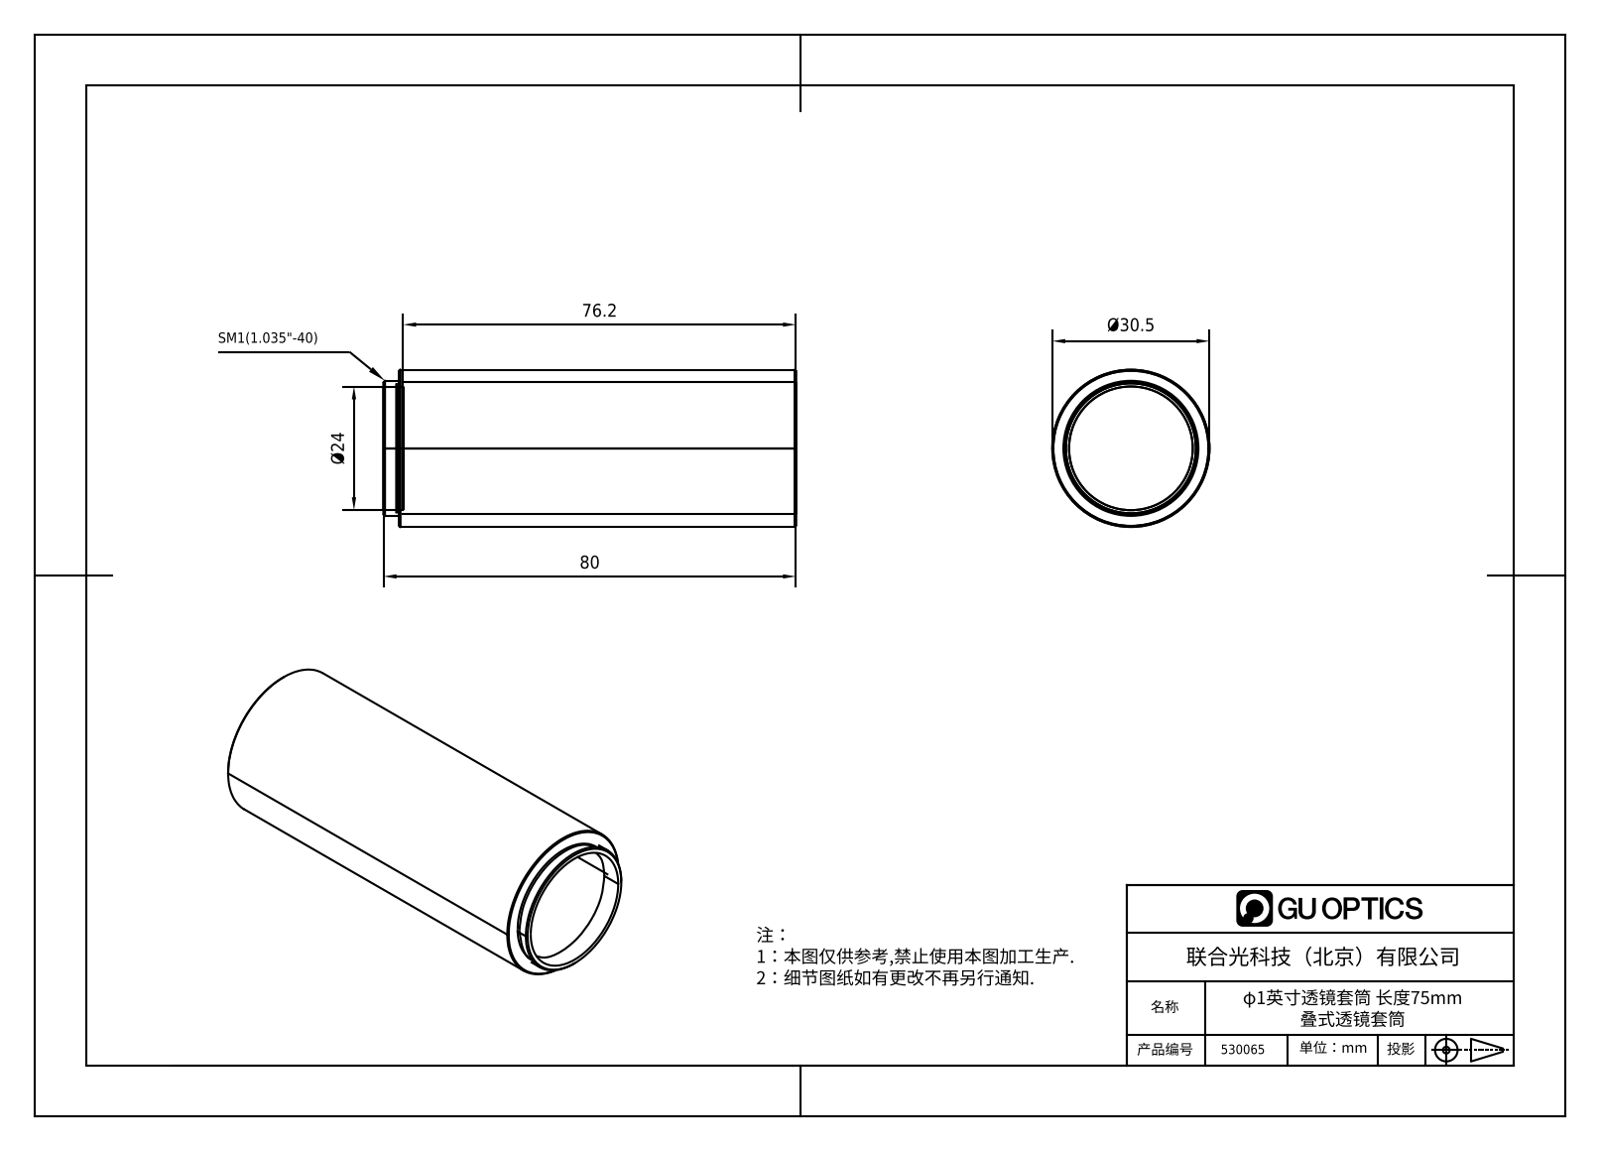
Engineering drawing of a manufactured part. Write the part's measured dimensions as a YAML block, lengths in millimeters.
part_name: "1.7.1.13_ZTC-1-3.0_SM1标准型3.0英寸层叠式透镜套筒"
step_written_by: "SolidWorks 2018 (AUTOMOTIVE_DESIGN)"
units: millimeters
bodies: {solids: 0, faces: 34, planar: 11, cylindrical: 12, other: 11}
overall_size: [80, 30.5, 30.5]
round_holes:
  - {diameter: 23.01, count: 1}
  - {diameter: 24, count: 1}
  - {diameter: 25.65, count: 1}
round_bosses_or_shafts:
  - {diameter: 30.5, count: 1}
  - {diameter: 26.2, count: 1}
  - {diameter: 25.2, count: 1}
face_to_face_distances: [77, 2.68, 74.32, 80, 77.32, 3, 3.38, 0.7, 73.62, 76.62]
